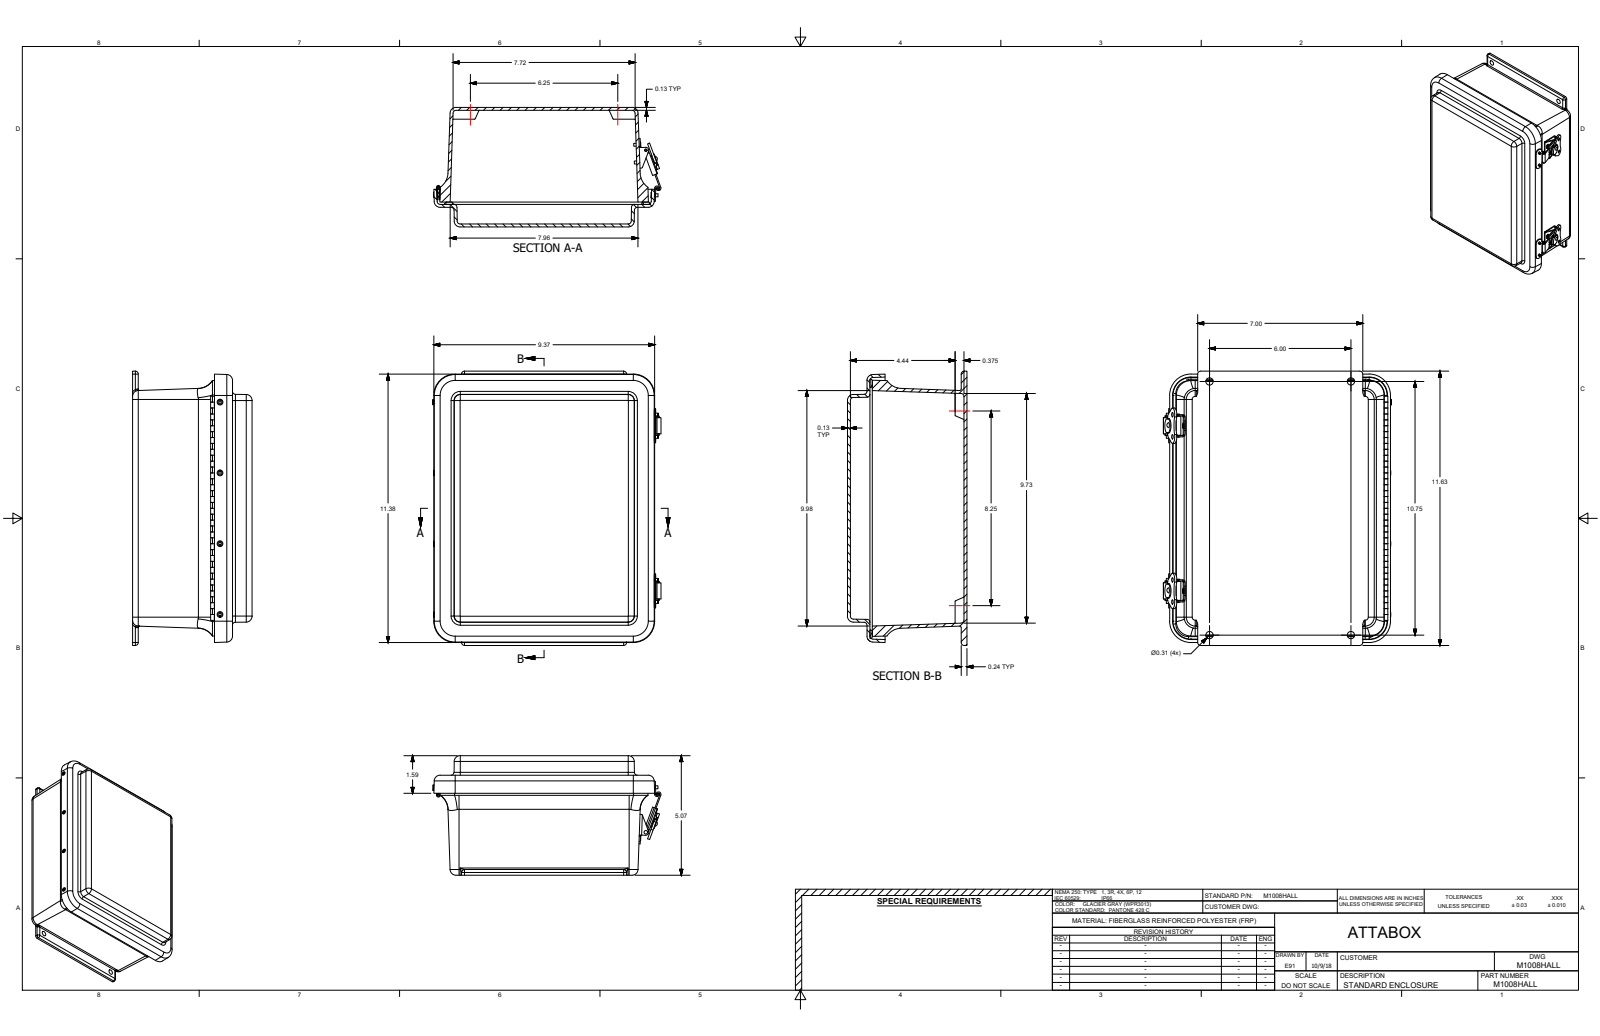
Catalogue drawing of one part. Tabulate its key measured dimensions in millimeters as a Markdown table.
| quantity | value |
| --- | --- |
| part name | M1008HALL |
| STEP written by | SolidWorks 2018 (AUTOMOTIVE_DESIGN) |
| units | millimeters |
| bodies | 46 solids, 1147 faces (466 planar, 469 cylindrical, 212 other) |
| overall size | 295.4 × 244.9 × 128.6 |
| volume | 1 016 000 mm³ |
| surface area | 570 300 mm² |
| round holes (diameter × count) | 3.6 × 18, 2.6 × 16, 3.3 × 8, 3.9 × 8, 3.3 × 4, 3.4 × 4, 4 × 4, 4.7 × 4, 5.5 × 4, 7.9 × 4, 3.4 × 2, 4.8 × 2 |
| round bosses / shafts (diameter × count) | 3.2 × 12, 3.2 × 6, 6.9 × 4, 16.8 × 2, 14.8 × 2, 13.3 × 2, 7.3 × 2, 5.4 × 2 |
| partial cylindrical surfaces (radius × count) | 0.8 × 36, 3.2 × 31, 0.4 × 16, 6.4 × 14, 1.5 × 13, 0.3 × 8, 0.5 × 8, 1.4 × 8 |
| main face-to-face distances | 3.2, 3.2, 125.4, 122.3, 128.6, 125.4, 104.4, 101.2, 21.1, 24.2 |
| hole center spacings | 152.4, 177.8, 76.2, 63.5, 19.1, 158.8, 178.8, 88.9 |
